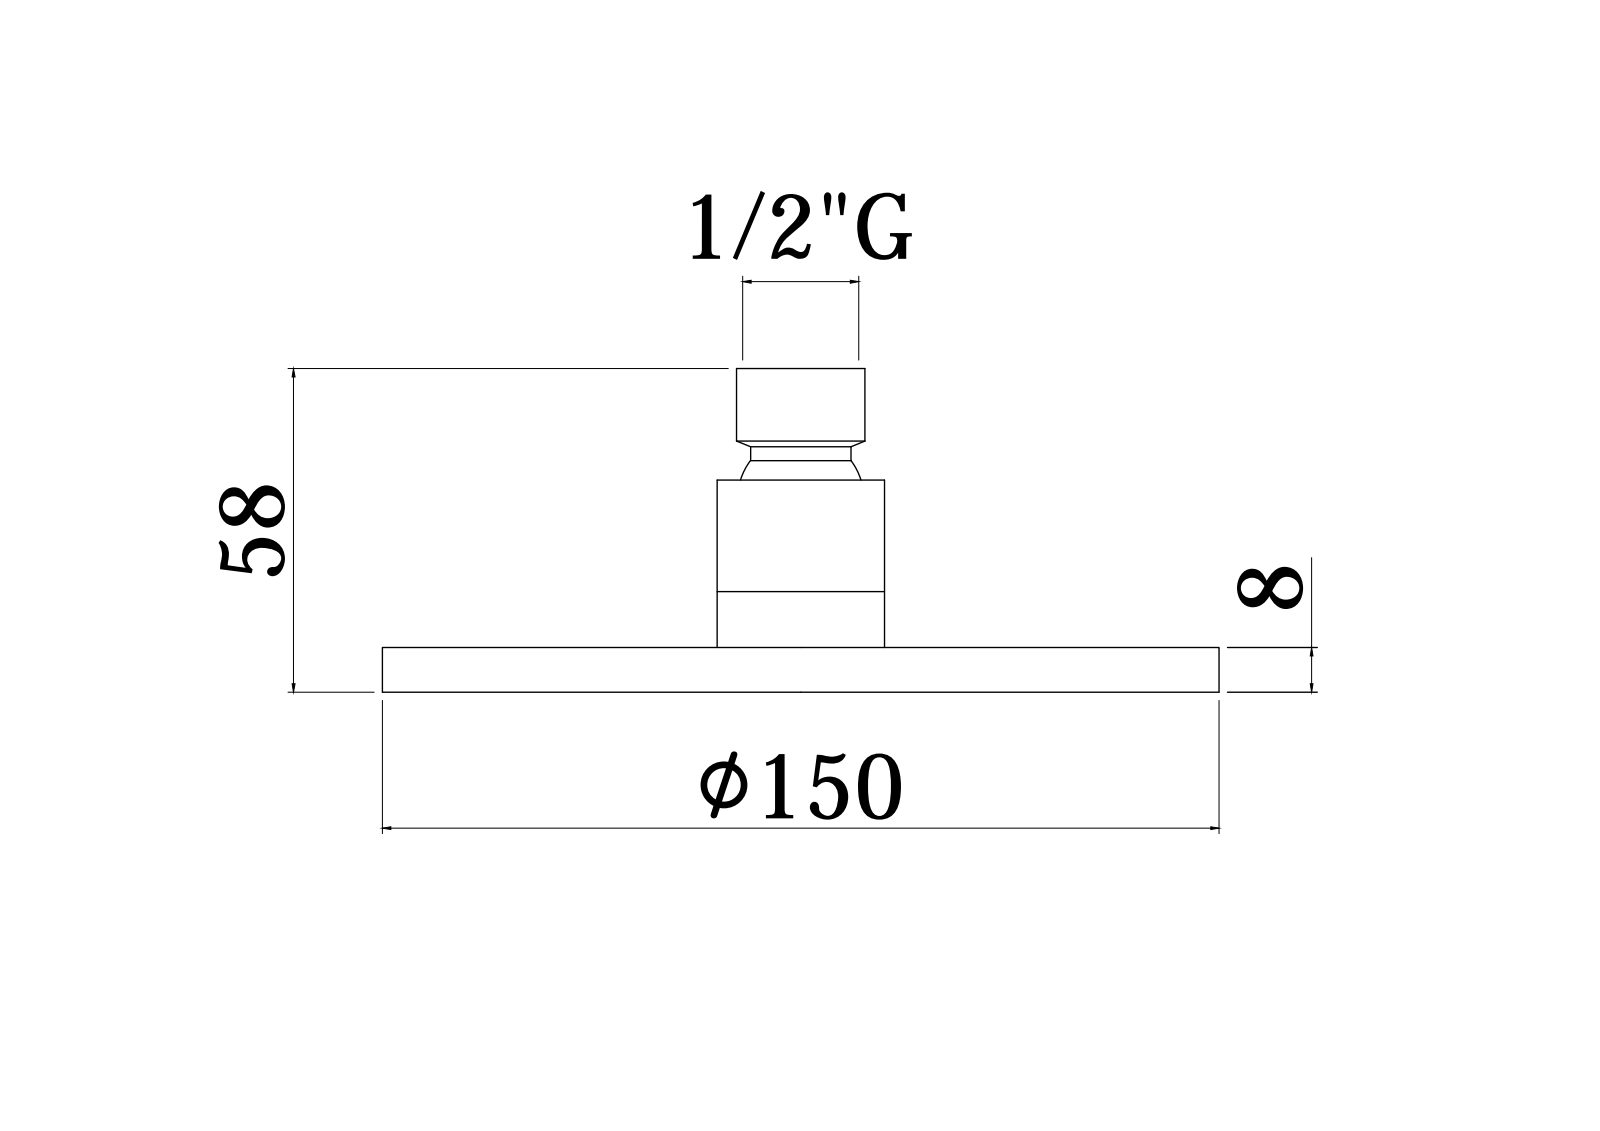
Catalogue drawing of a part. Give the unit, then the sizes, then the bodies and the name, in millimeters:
Units: millimetres
Overall size (bounding box): 150.2 × 150.2 × 51.9
Round holes (diameter × count): ⌀1.5 ×42, ⌀1.7 ×42, ⌀7 ×7, ⌀2.5 ×6, ⌀5.1 ×6, ⌀6 ×6, ⌀15 ×1, ⌀16 ×1, ⌀16.5 ×1, ⌀18.63 ×1, ⌀23.1 ×1, ⌀23.8 ×1
Round bosses / shafts (diameter × count): ⌀10 ×42, ⌀5 ×6, ⌀150.2 ×1, ⌀150 ×1, ⌀145.2 ×1, ⌀31.8 ×1, ⌀28 ×1, ⌀23.2 ×1
Partial cylindrical surfaces — rounded edges, fillets, slot ends (radius × count): R18.2 ×12, R8.5 ×6, R20 ×6, R67.2 ×1
Main face-to-face distances: 8.5, 7.5, 1, 1.5, 7, 6, 5.6, 2.9, 1.4, 4.6
Hole centre spacings: 44.44, 15, 35, 50, 30, 73.99, 18.59, 25.06
Volume: 86 396 mm³ · Surface area: 85 311 mm²
Bodies: 1 solid, 2117 faces (196 planar, 402 cylindrical, 1519 other)
Part name (STEP PRODUCT): ZSOF092CR
STEP written by: CREO PARAMETRIC BY PTC INC, 2020044 (CONFIG_CONTROL_DESIGN)
